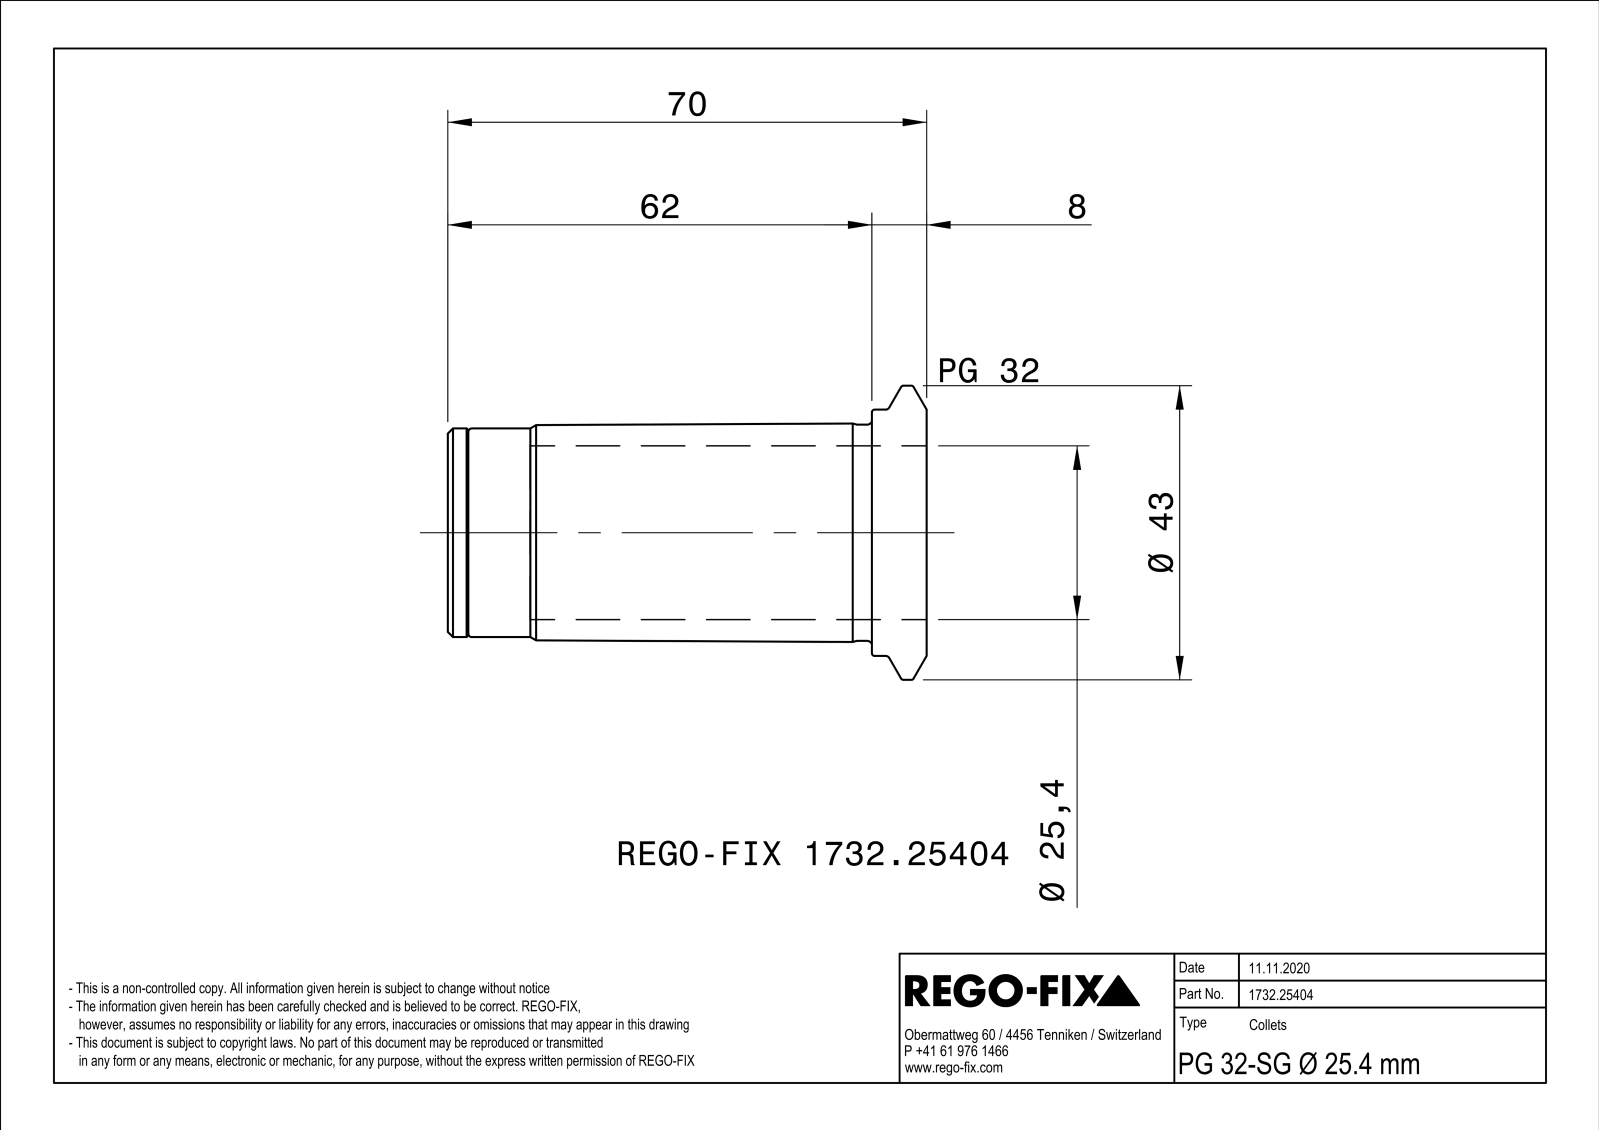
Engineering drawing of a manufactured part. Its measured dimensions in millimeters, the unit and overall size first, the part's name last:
Units: millimetres
Overall size (bounding box): 70 × 43 × 42.99
Round holes (diameter × count): ⌀4 ×3, ⌀8.92 ×1, ⌀10.5 ×1, ⌀25.4 ×1, ⌀26.92 ×1, ⌀28.5 ×1
Round bosses / shafts (diameter × count): ⌀43 ×1, ⌀36 ×1, ⌀31.6 ×1, ⌀30.5 ×1, ⌀26.5 ×1, ⌀21 ×1
Partial cylindrical surfaces — rounded edges, fillets, slot ends (radius × count): R2 ×6, R3.5 ×3, R3.98 ×1, R4.75 ×1, R8.75 ×1
Main face-to-face distances: 1, 70, 58, 12, 59, 11, 8, 60, 2, 10
Hole centre spacings: 7.75, 13.42, 13.43
Volume: 25 920 mm³ · Surface area: 16 439 mm²
Bodies: 1 solid, 125 faces (31 planar, 40 cylindrical, 54 other)
Part name (STEP PRODUCT): NOCUT
STEP written by: SIEMENS PLM Software Solid Edge ST10 (AUTOMOTIVE_DESIGN)
